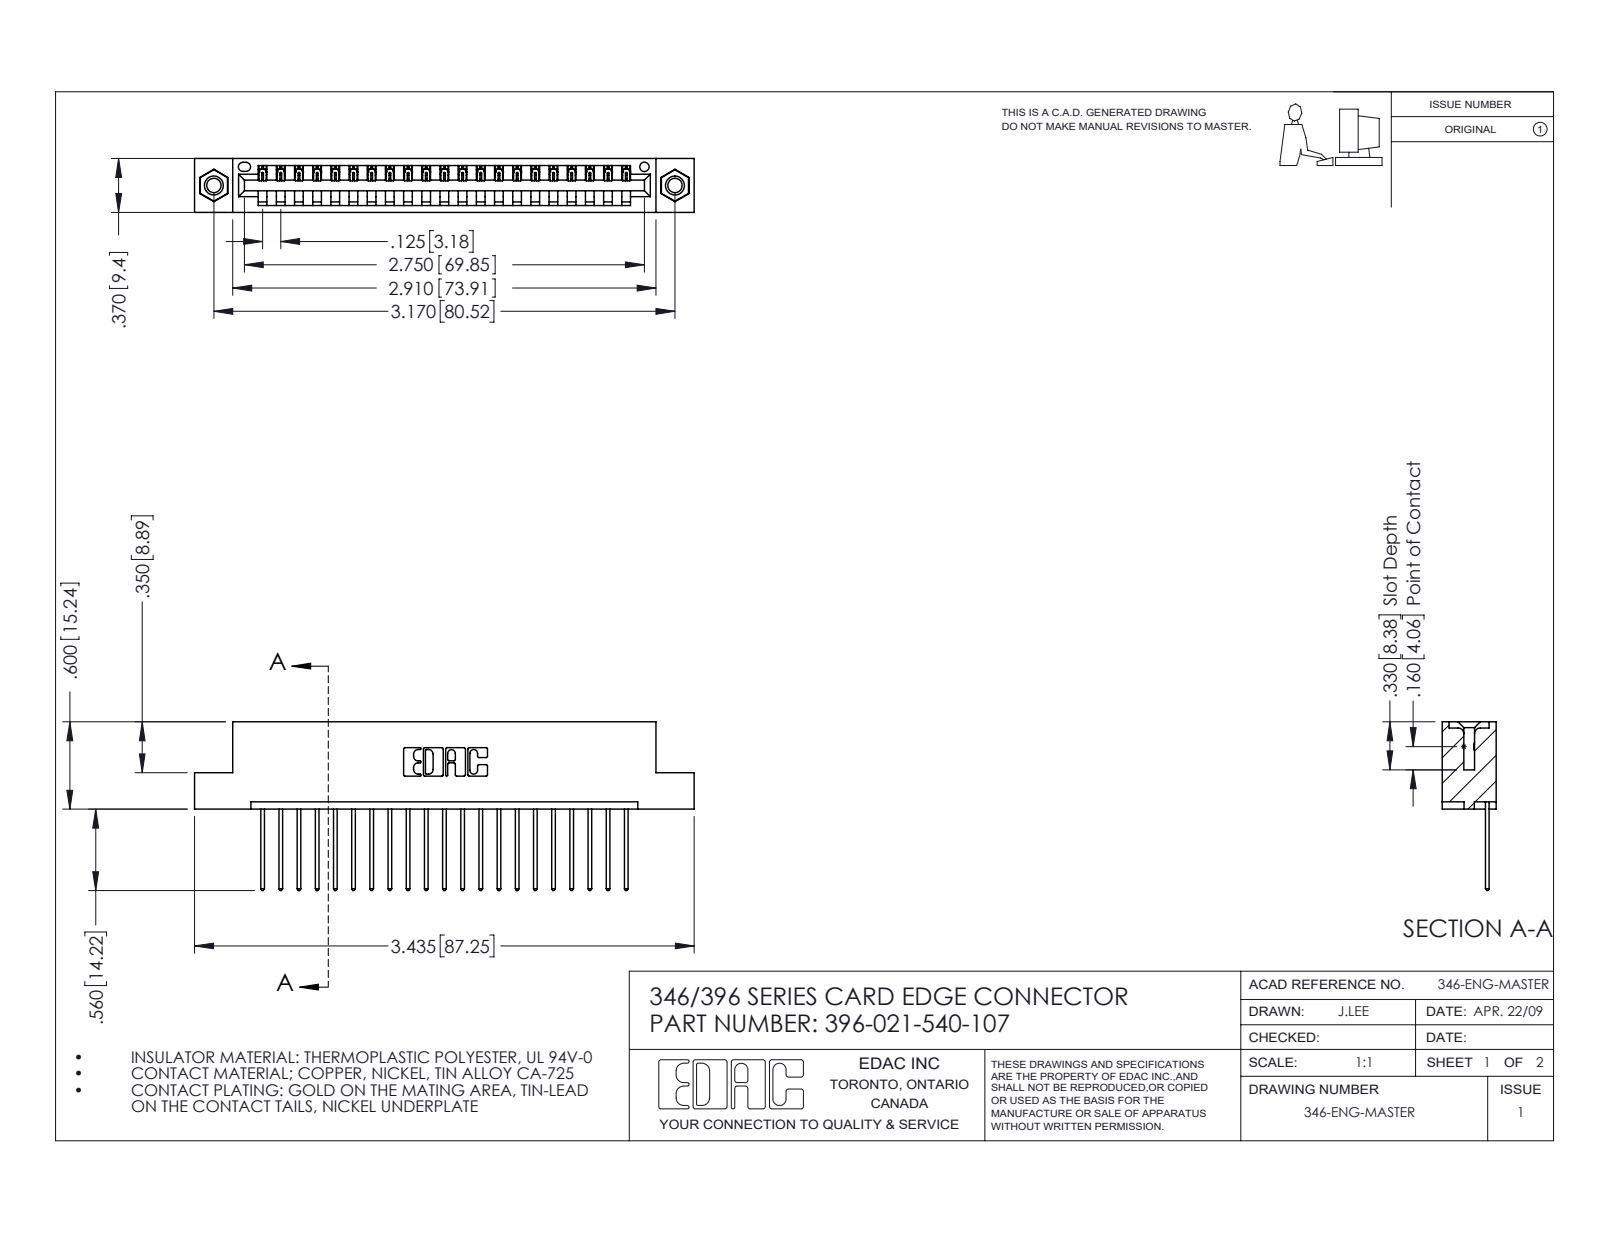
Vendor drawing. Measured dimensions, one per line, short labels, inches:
name: 345-250-001_345-250-005-103; 396-021-540-107; 345-292-001_345-293-140; 346 Part_Flush Mounting Lugs - 0.156 Dia-TI
written by: SolidWorks 2016 (CONFIG_CONTROL_DESIGN)
unit: in
bodies: 24 solids, 1400 faces (948 planar, 436 cylindrical, 16 other)
size: 3.435 × 1.16 × 0.37
volume: 0.502 in³; area: 15.95 in²
holes: 2× ⌀0.098, 2× ⌀0.125, 2× ⌀0.156, 1× ⌀0.064
bosses: 2× ⌀0.155
rounds: 42× R0.006, 42× R0.01, 22× R0.01, 6× R0.007, 6× R0.031, 3× R0.026, 2× R0.031, 2× R0.04
face distances: 0.048, 0.322, 0.25, 0.37, 0.072, 0.298, 0.025, 0.148, 0.222, 0.1
hole spacings: 0.246, 2.963, 3.17
